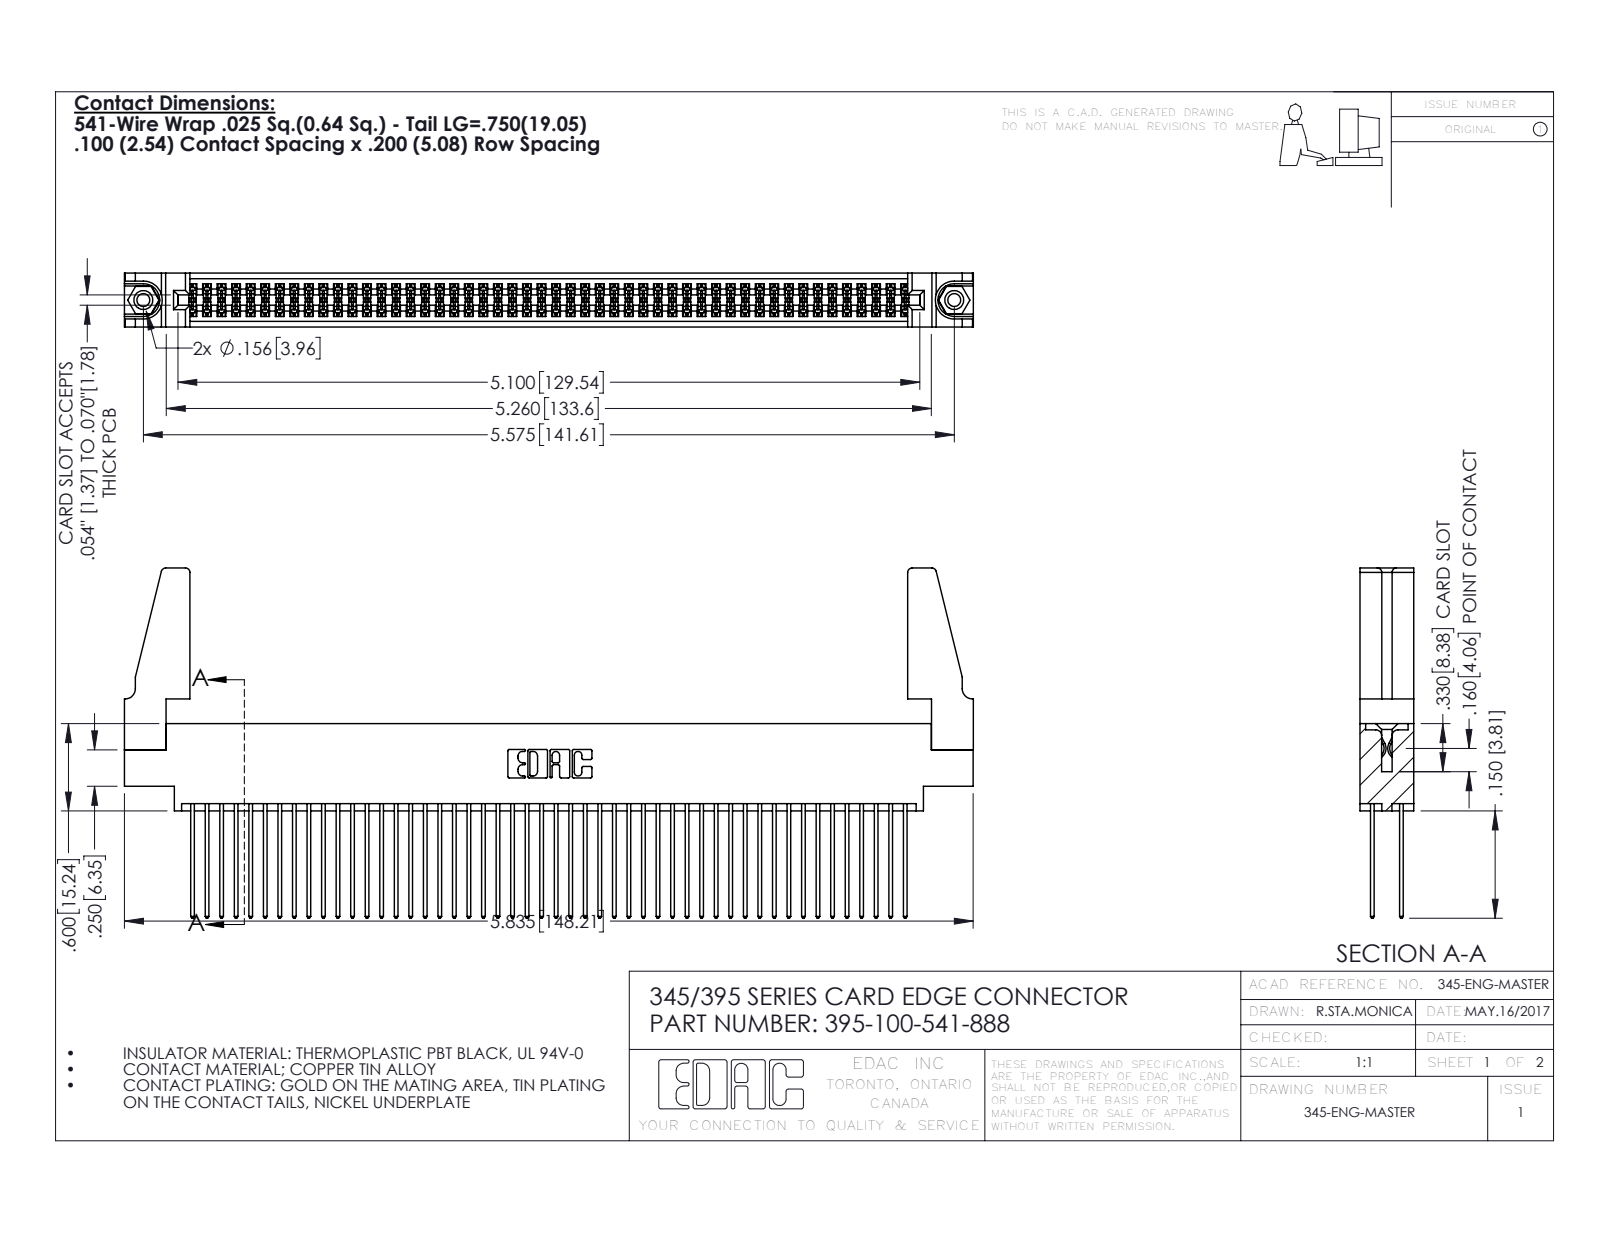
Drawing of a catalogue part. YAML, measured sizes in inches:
part_name: "345-220-078_345-220-088; 345-292-001_345-293-141; 345-250-001_345-250-001-102; 345 Part_0.170 Offset - 0.156 Dia-TH (+1 more)"
step_written_by: "SolidWorks 2016 (CONFIG_CONTROL_DESIGN)"
units: inches
bodies: {solids: 105, faces: 5254, planar: 3456, cylindrical: 1782, other: 16}
overall_size: [5.836, 2.407, 0.37]
volume: 1.11
surface_area: 43.7
round_holes:
  - {diameter: 0.089, count: 2}
  - {diameter: 0.125, count: 2}
  - {diameter: 0.156, count: 2}
  - {diameter: 0.064, count: 1}
round_bosses_or_shafts:
  - {diameter: 0.155, count: 2}
partial_cylinders:
  - {radius: 0.006, count: 150}
  - {radius: 0.01, count: 100}
  - {radius: 0.01, count: 22}
  - {radius: 0.03, count: 8}
  - {radius: 0.007, count: 6}
  - {radius: 0.031, count: 6}
  - {radius: 0.026, count: 3}
  - {radius: 0.014, count: 2}
face_to_face_distances: [0.072, 0.298, 0.098, 0.272, 0.025, 0.2, 0.37, 0.225, 0.175, 0.149]
hole_center_spacings: [0.27, 5.339, 5.575]
